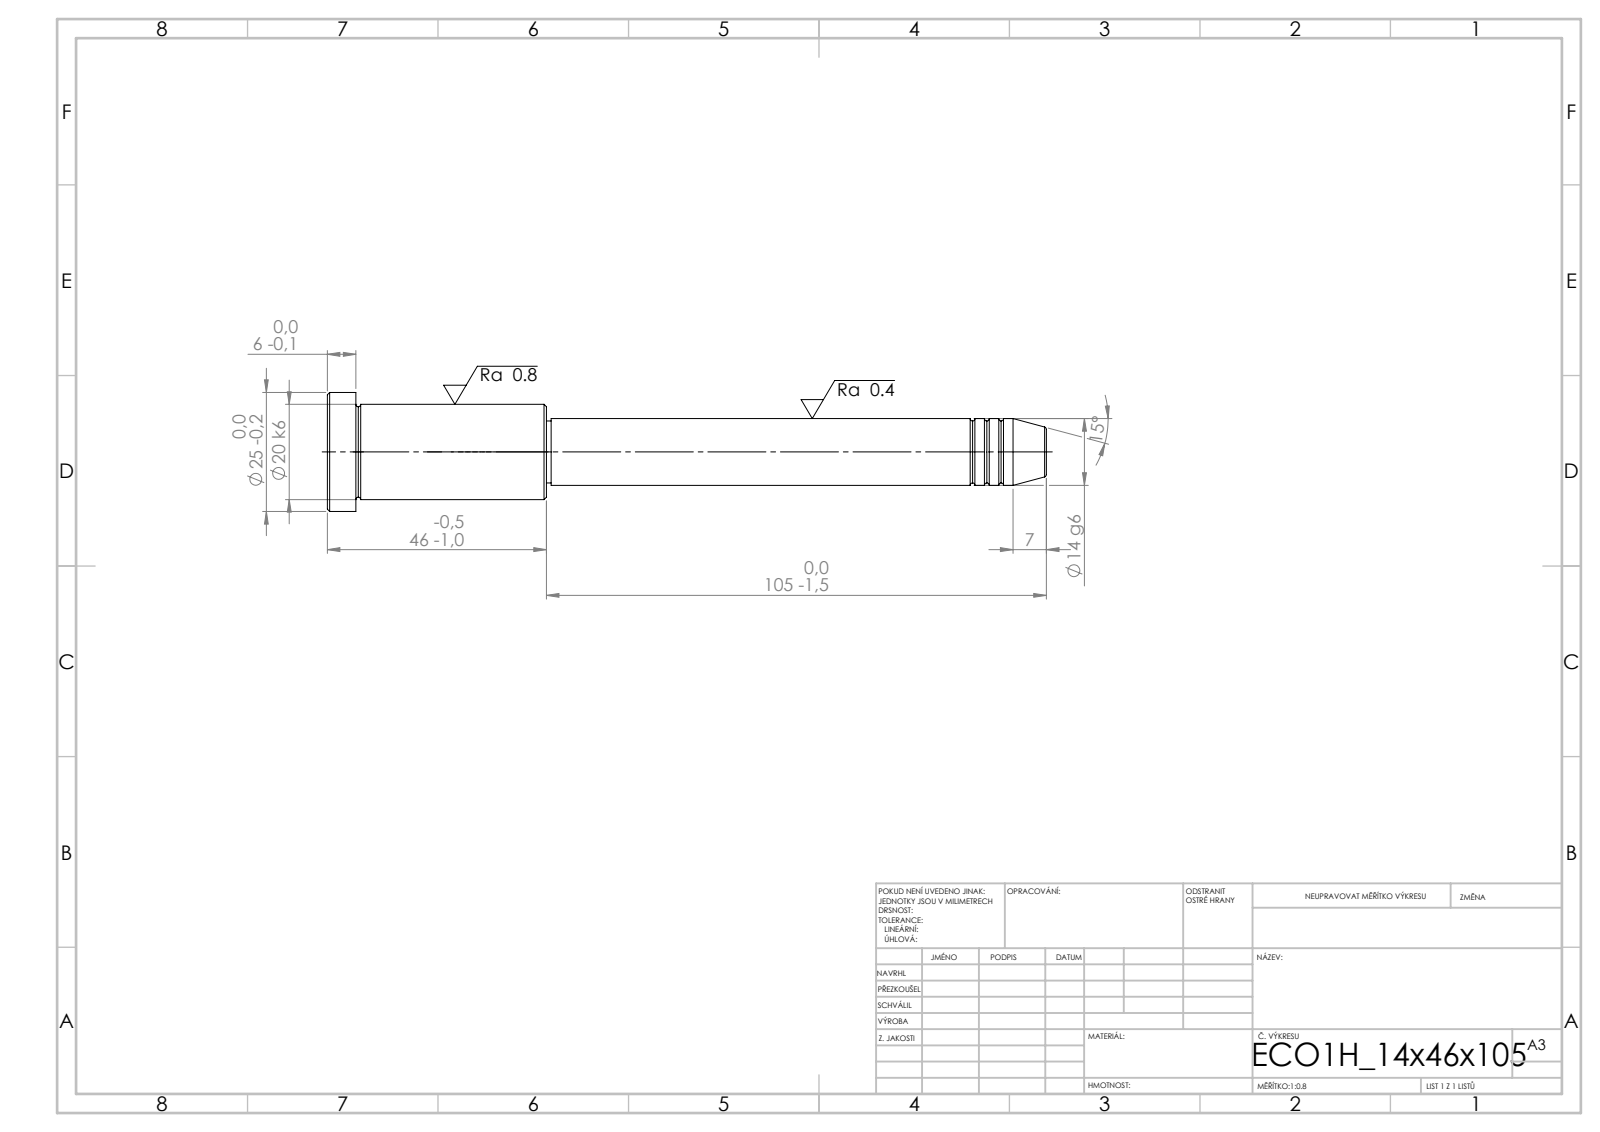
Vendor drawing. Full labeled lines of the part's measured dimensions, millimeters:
STEP written by: SolidWorks 2019 (CONFIG_CONTROL_DESIGN)
Units: millimetres
Bodies: 1 solid, 43 faces (5 planar, 14 cylindrical, 24 other)
Overall size (bounding box): 151 × 25 × 25
Volume: 31 298 mm³ · Surface area: 8 573 mm²
Round bosses / shafts (diameter × count): ⌀25 ×1, ⌀20 ×1, ⌀14 ×1, ⌀13 ×1
Main face-to-face distances: 6, 40, 46, 105, 145, 151, 104, 1, 41, 47
